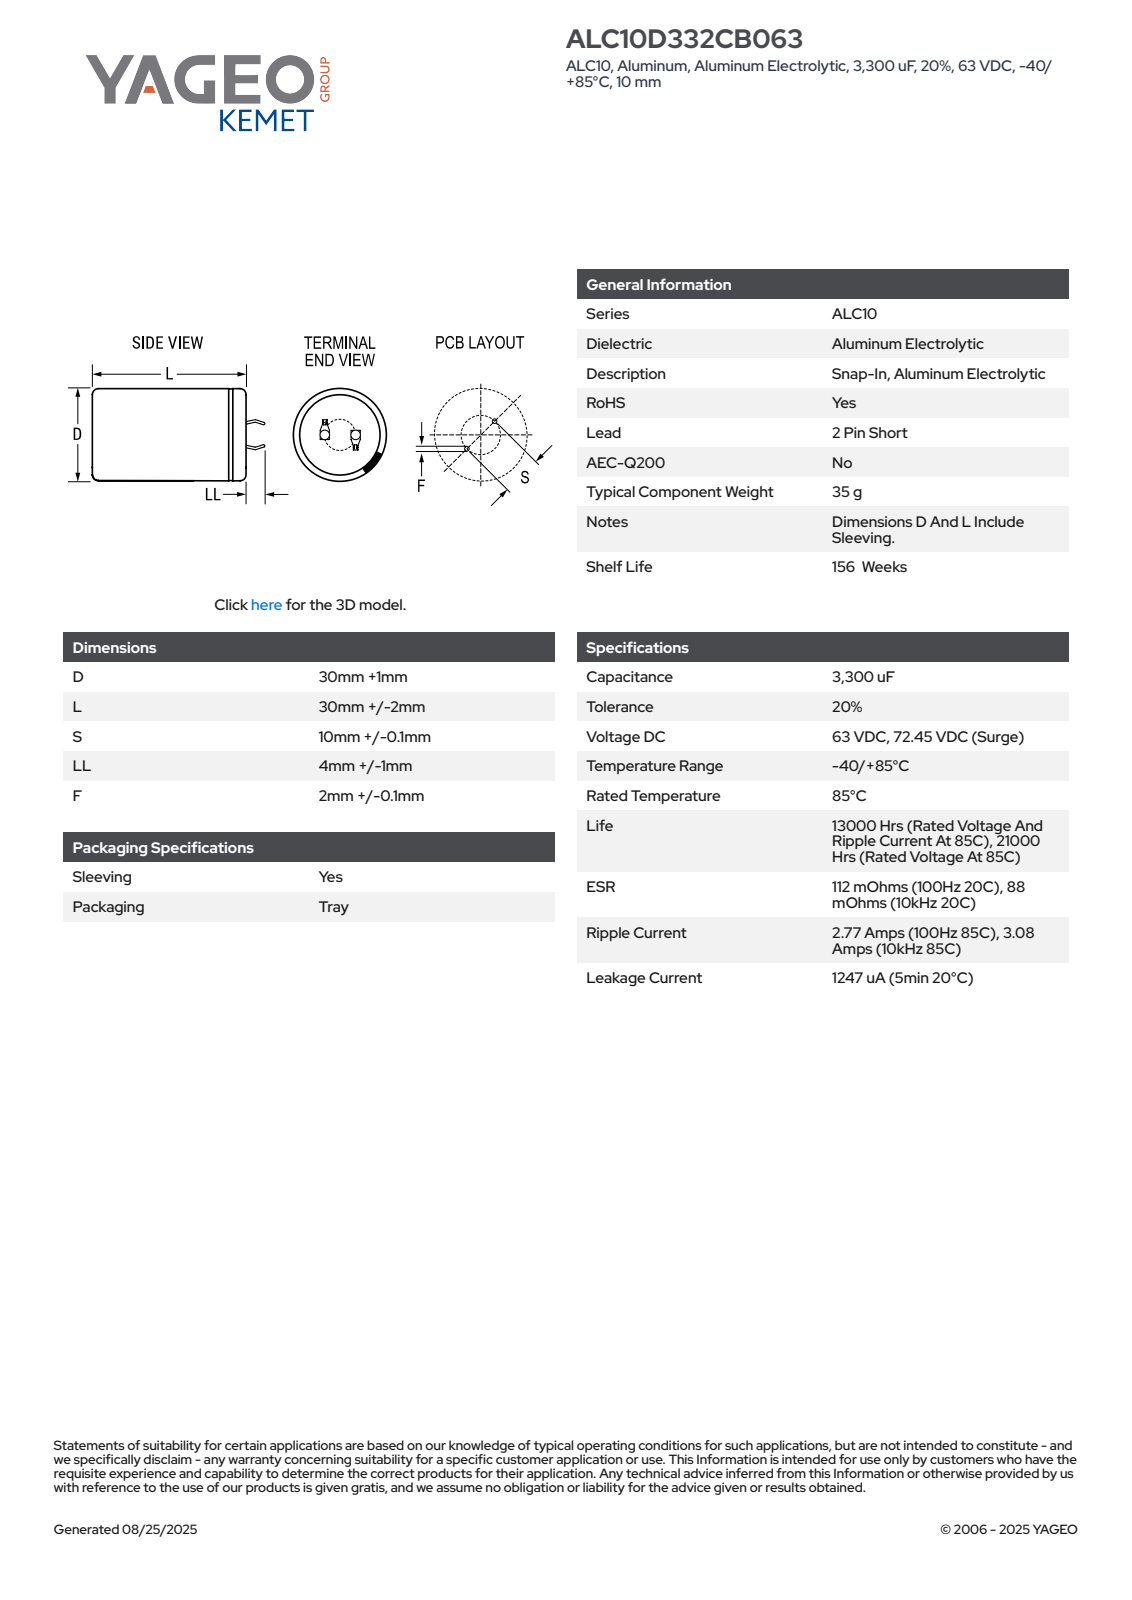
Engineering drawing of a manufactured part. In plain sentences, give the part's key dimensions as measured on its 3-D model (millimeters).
The part is named "CARS_K2P_30X30_D31L32S10LL5F2.1". Its 3-D file was written by "SolidWorks 2014 (AUTOMOTIVE_DESIGN)". It is 1 solid with 100 faces: 52 planar, 9 cylindrical and 39 other. Overall it measures 36.99 by 31 by 31 millimeters. Its volume is 23 817 cubic millimeters and its surface area 4 625 square millimeters. Round holes: 1 of diameter 27.43. Round bosses or shafts: 1 of diameter 31. Partial cylindrical surfaces (rounded edges, fillets, slot ends): 1 of radius 15.49. The main face-to-face distances are 31.99, 32.49, 0.5, 7.08, 0.6, 0.59, 7.6, 0.75, 1.35, 7.68.
